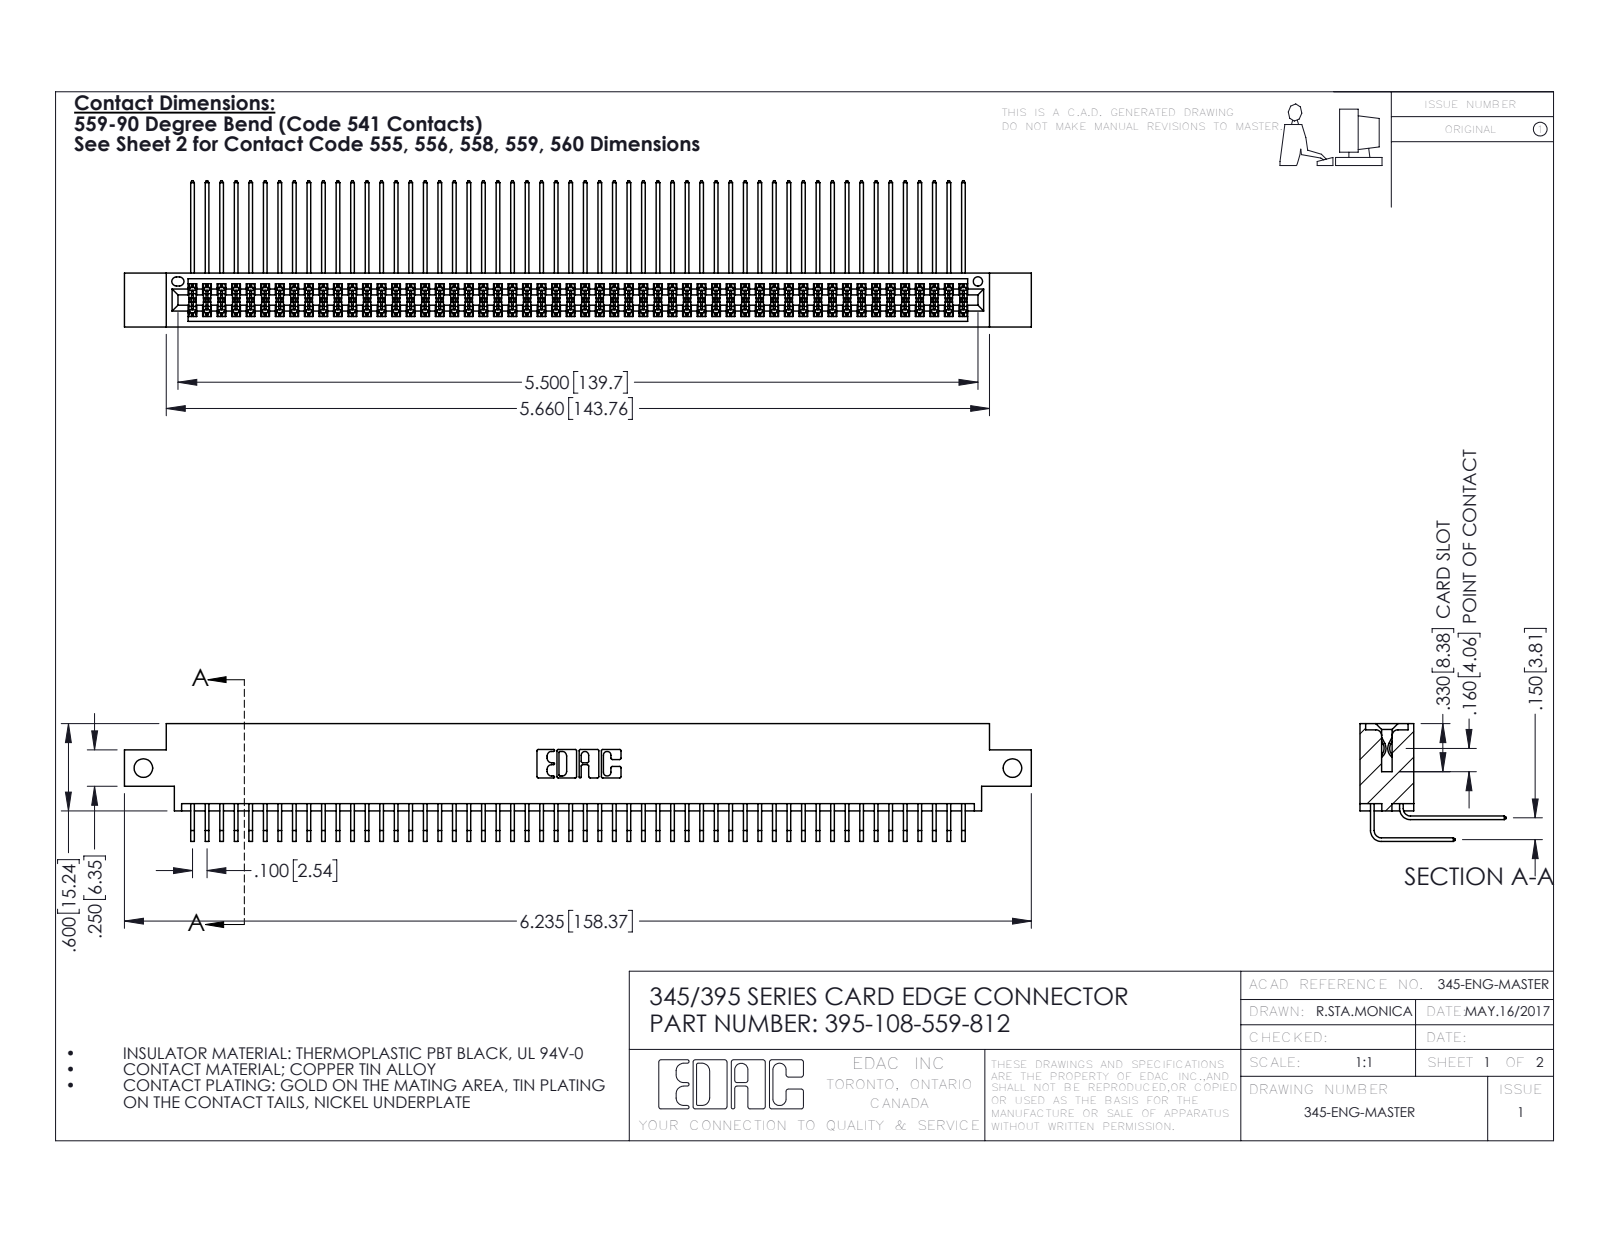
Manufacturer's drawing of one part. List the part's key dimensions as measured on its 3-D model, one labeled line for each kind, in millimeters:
Part name (STEP PRODUCT): 345 Part_0.170 Offset - Side Mount; 395-108-559-812; 345-292-001_559 Tail - 2; 345-292-001_558 559 Tail - 1
STEP written by: SolidWorks 2016 (CONFIG_CONTROL_DESIGN)
Units: millimetres
Bodies: 109 solids, 5746 faces (3864 planar, 1882 cylindrical, 0 other)
Overall size (bounding box): 158.4 × 25.5 × 20.5
Volume: 15 900 mm³ · Surface area: 26 700 mm²
Round holes (diameter × count): ⌀3.3 ×2, ⌀1.6 ×1
Partial cylindrical surfaces — rounded edges, fillets, slot ends (radius × count): R0.2 ×162, R0.3 ×22, R0.2 ×6, R0.8 ×6, R0.7 ×3, R0.4 ×2, R0.5 ×2, R0.6 ×2
Main face-to-face distances: 1.8, 7.6, 9.4, 5.1, 2.5, 6.9, 0.6, 5.7, 4.4, 3.8
Hole centre spacings: 151.8
